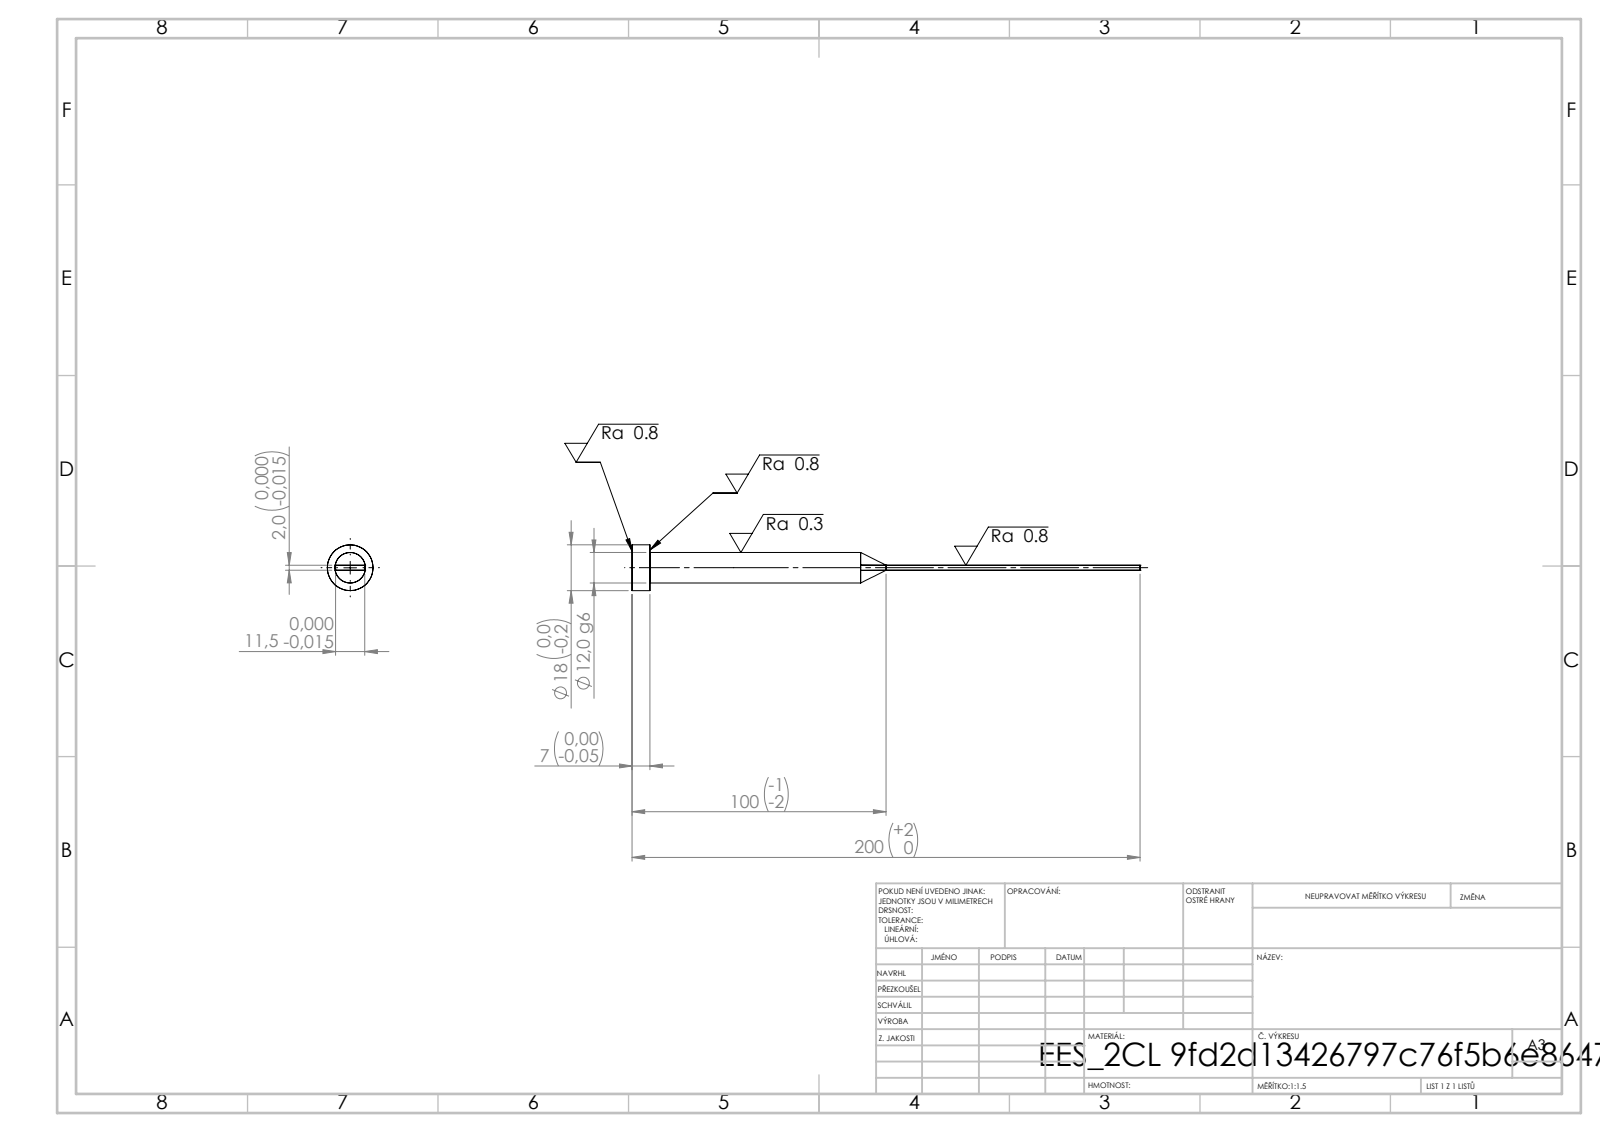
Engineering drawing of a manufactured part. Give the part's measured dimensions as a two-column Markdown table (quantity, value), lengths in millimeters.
| quantity | value |
| --- | --- |
| STEP written by | SolidWorks 2019 (CONFIG_CONTROL_DESIGN) |
| units | millimeters |
| bodies | 1 solid, 15 faces (7 planar, 4 cylindrical, 4 other) |
| overall size | 200 × 18 × 18 |
| volume | 14 114 mm³ |
| surface area | 6 969 mm² |
| round bosses / shafts (diameter × count) | 18 × 1, 12 × 1 |
| main face-to-face distances | 2, 11.5, 7, 200, 193 |
